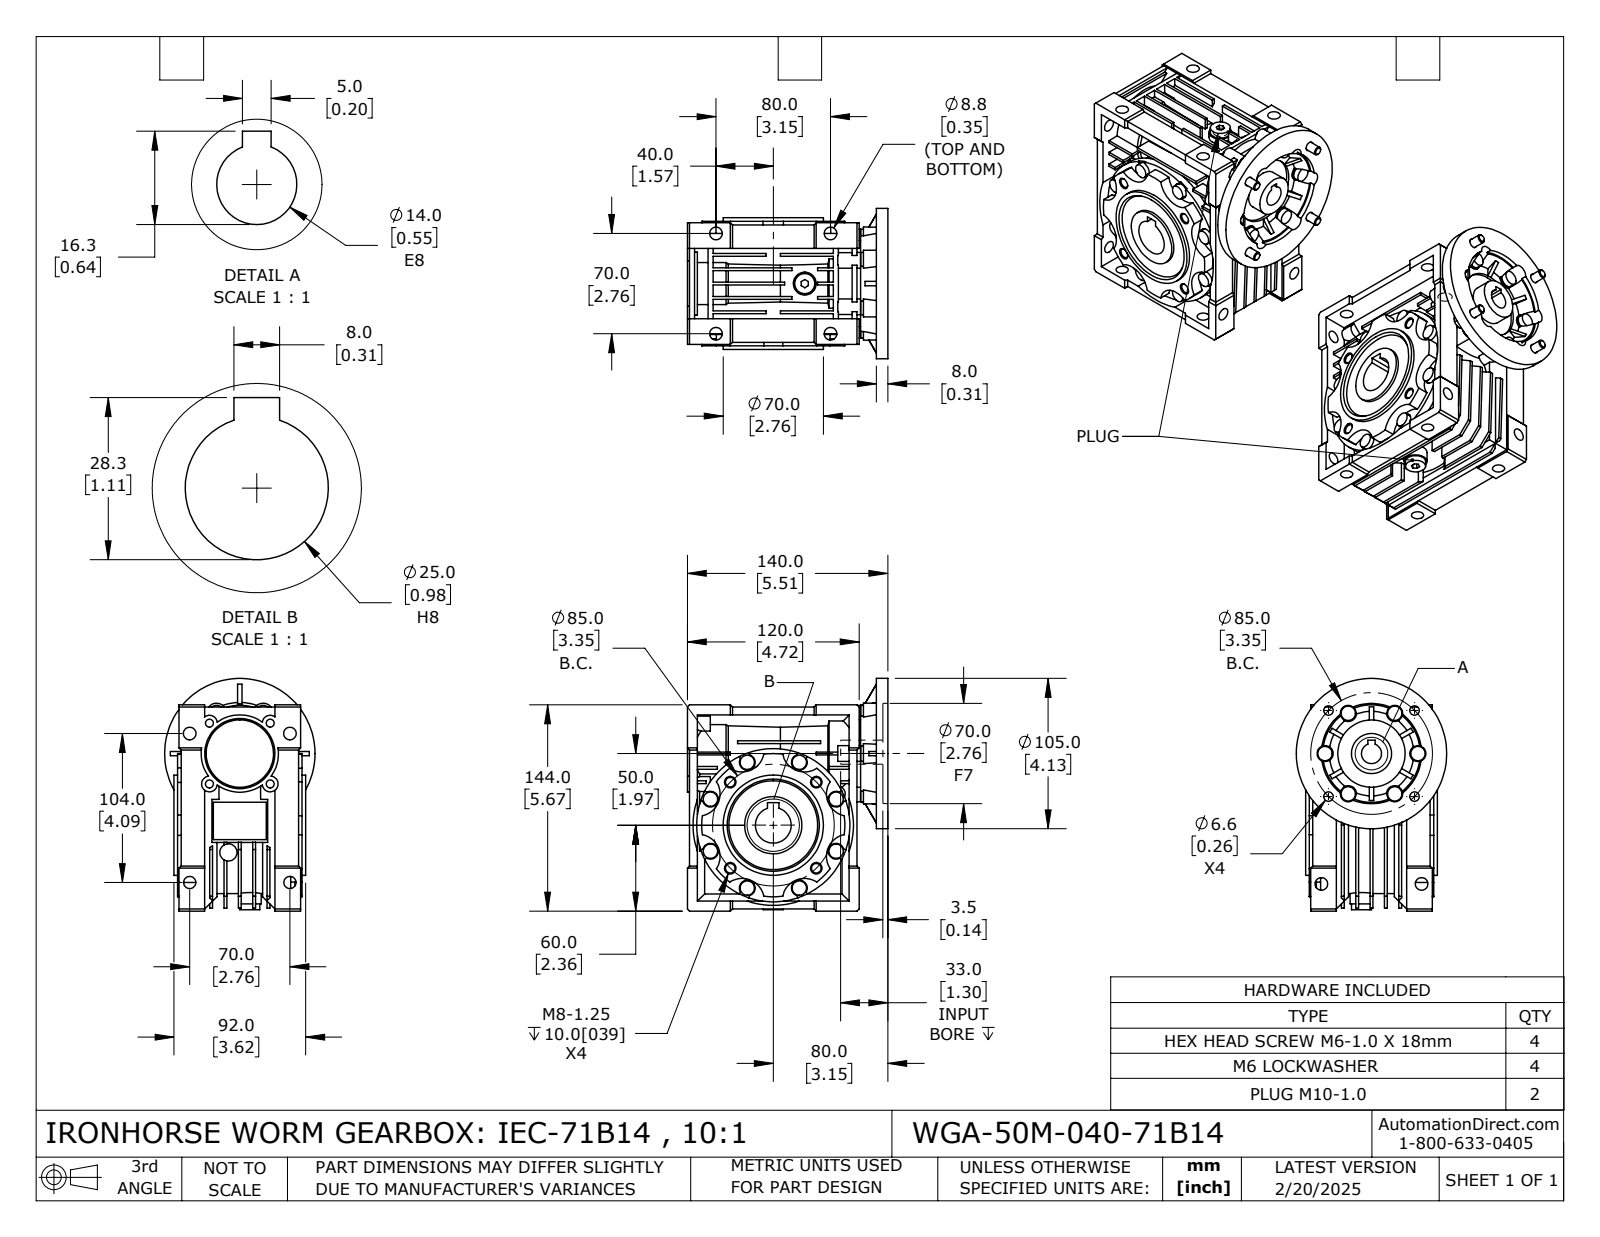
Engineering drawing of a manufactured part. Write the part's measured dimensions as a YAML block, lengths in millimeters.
part_name: "WGA-50M-040-71B14"
step_written_by: "SolidWorks 2024 (CONFIG_CONTROL_DESIGN)"
units: millimeters
bodies: {solids: 15, faces: 1132, planar: 615, cylindrical: 372, other: 145}
overall_size: [162.5, 148.5, 105]
volume: 1065000
surface_area: 235209
round_holes:
  - {diameter: 8.8, count: 8}
  - {diameter: 8.5, count: 6}
  - {diameter: 5.55, count: 4}
  - {diameter: 6.1, count: 4}
  - {diameter: 6.6, count: 4}
  - {diameter: 6.65, count: 2}
  - {diameter: 6.65, count: 2}
  - {diameter: 9, count: 2}
  - {diameter: 14, count: 1}
  - {diameter: 15, count: 1}
  - {diameter: 25, count: 1}
  - {diameter: 28, count: 1}
round_bosses_or_shafts:
  - {diameter: 10, count: 14}
  - {diameter: 12.2, count: 4}
  - {diameter: 6, count: 4}
  - {diameter: 16, count: 2}
  - {diameter: 14, count: 2}
  - {diameter: 9.8, count: 2}
  - {diameter: 8.3, count: 2}
  - {diameter: 107, count: 1}
partial_cylinders:
  - {radius: 5.5, count: 18}
  - {radius: 6, count: 8}
  - {radius: 15, count: 8}
  - {radius: 15.5, count: 8}
  - {radius: 5.75, count: 6}
  - {radius: 7, count: 6}
  - {radius: 20.76, count: 1}
  - {radius: 35, count: 1}
face_to_face_distances: [8, 2, 10, 7, 1.5, 5.5, 20, 12, 55, 35]
hole_center_spacings: [42.5, 52.02, 60.1, 70, 12.5, 30, 42.42, 72.49]
